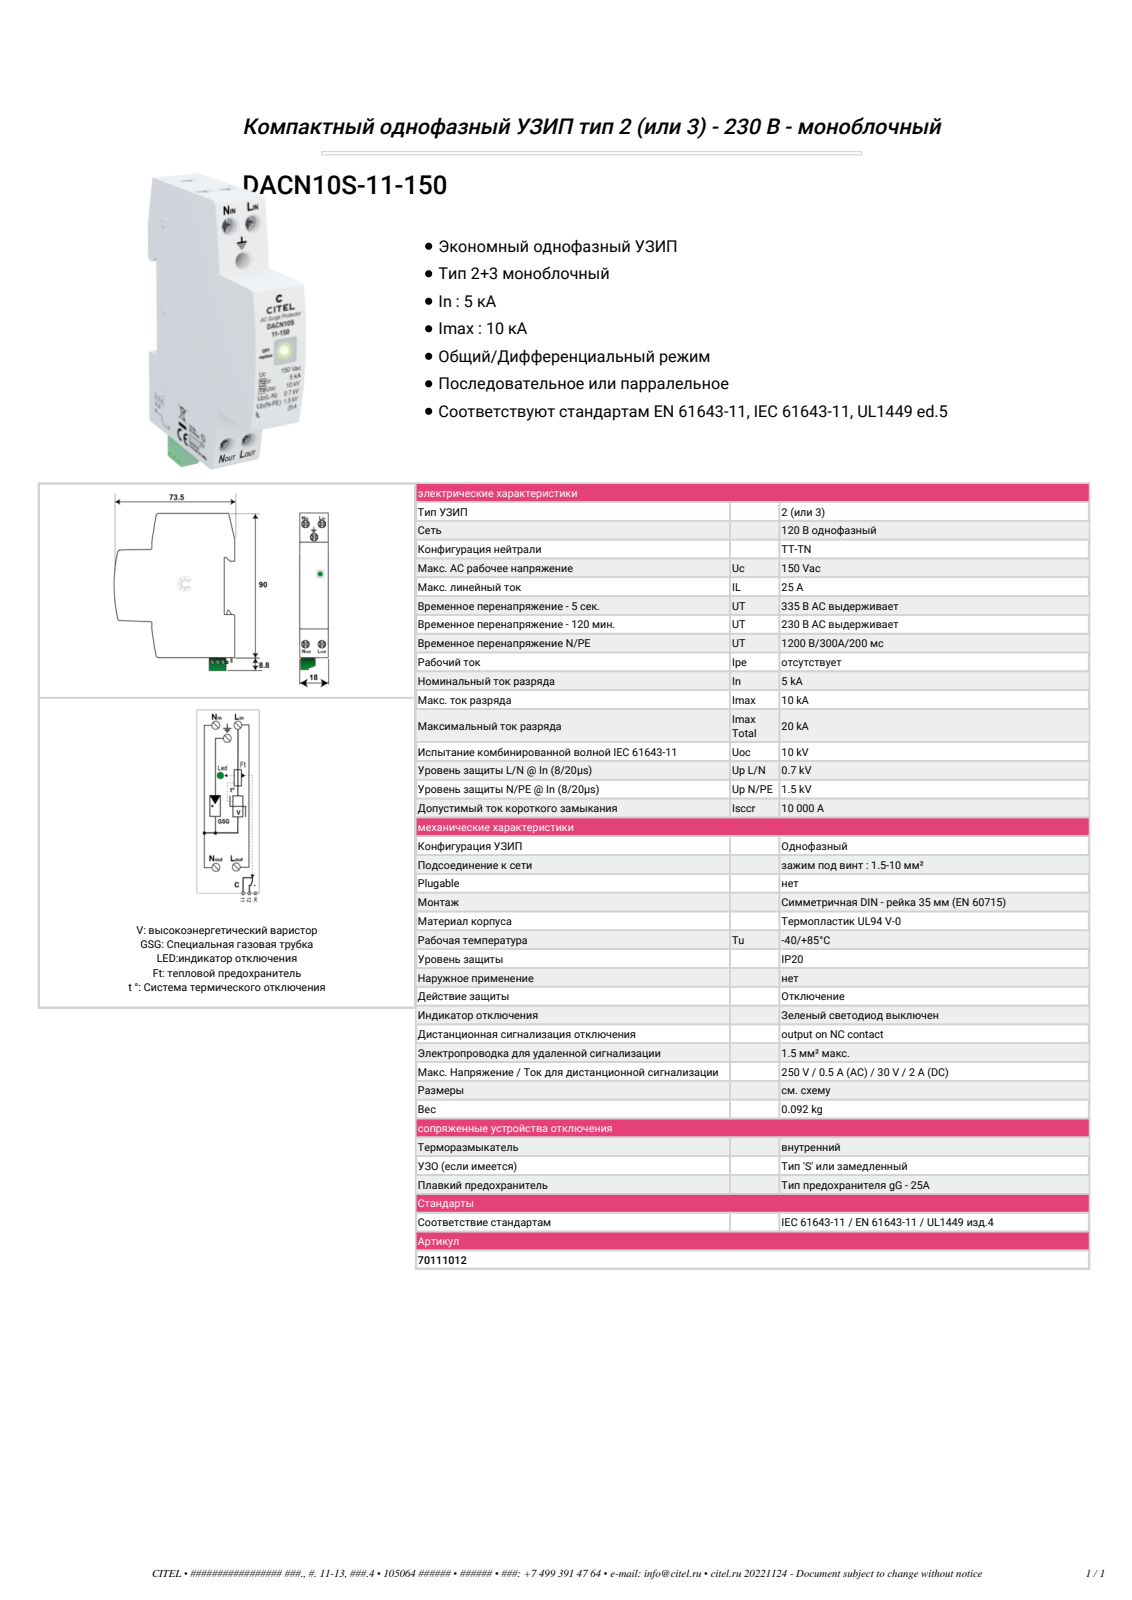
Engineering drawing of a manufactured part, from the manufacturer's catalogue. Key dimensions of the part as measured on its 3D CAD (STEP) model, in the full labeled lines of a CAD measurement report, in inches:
Part name (STEP PRODUCT): dacn10s-20-150
STEP written by: Spatial InterOp 3D (AP242_MANAGED_MODEL_BASED_3D_ENGINEERING_MIM_LF)
Units: inches
Bodies: 1 solid, 499 faces (425 planar, 72 cylindrical, 2 other)
Overall size (bounding box): 3.894 × 2.894 × 0.709
Volume: 5.619 in³ · Surface area: 30.31 in²
Round holes (diameter × count): ⌀0.209 ×5, ⌀0.114 ×3, ⌀0.157 ×1, ⌀0.354 ×1
Round bosses / shafts (diameter × count): ⌀0.108 ×3, ⌀0.315 ×1, ⌀0.122 ×1
Partial cylindrical surfaces — rounded edges, fillets, slot ends (radius × count): R0.059 ×5, R0.039 ×4, R0.083 ×3, R3.937 ×3, R0.03 ×2, R0.039 ×2, R0.061 ×2, R0.079 ×2
Main face-to-face distances: 0.709, 0.256, 2.657, 0.886, 3.543, 0.163, 0.197, 0.236, 0.419, 0.033
Hole centre spacings: 0.138, 0.327, 0.463, 2.446, 2.874, 2.893, 0.276, 0.887
